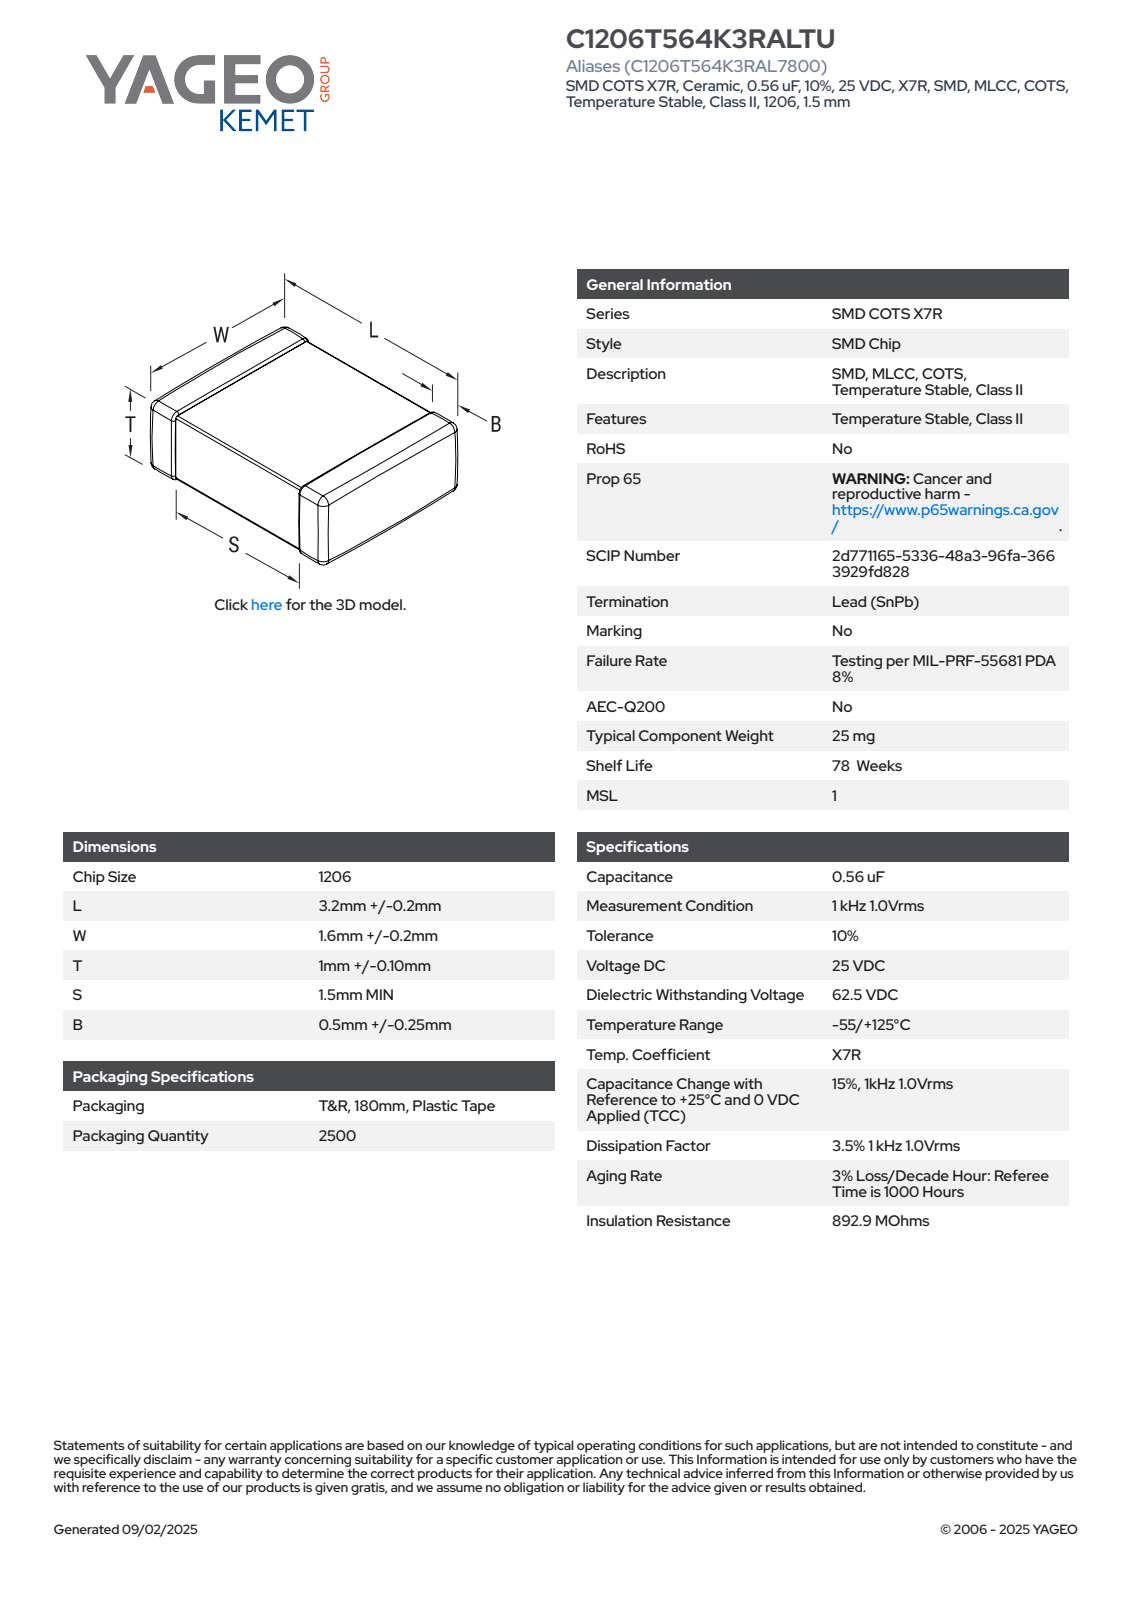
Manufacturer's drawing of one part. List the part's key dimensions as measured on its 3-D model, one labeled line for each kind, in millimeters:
Part name (STEP PRODUCT): CCSM_STD_1206_L3.4W1.8T1.1S1B0.75
STEP written by: SolidWorks 2021 (AUTOMOTIVE_DESIGN)
Units: millimetres
Bodies: 4 solids, 125 faces (71 planar, 38 cylindrical, 16 other)
Overall size (bounding box): 3.4 × 1.8 × 1.1
Volume: 6 mm³ · Surface area: 23 mm²
Main face-to-face distances: 1.06, 1.02, 1.76, 1.1, 1.72, 3.4, 1.8, 1.07, 1.03, 1.57
